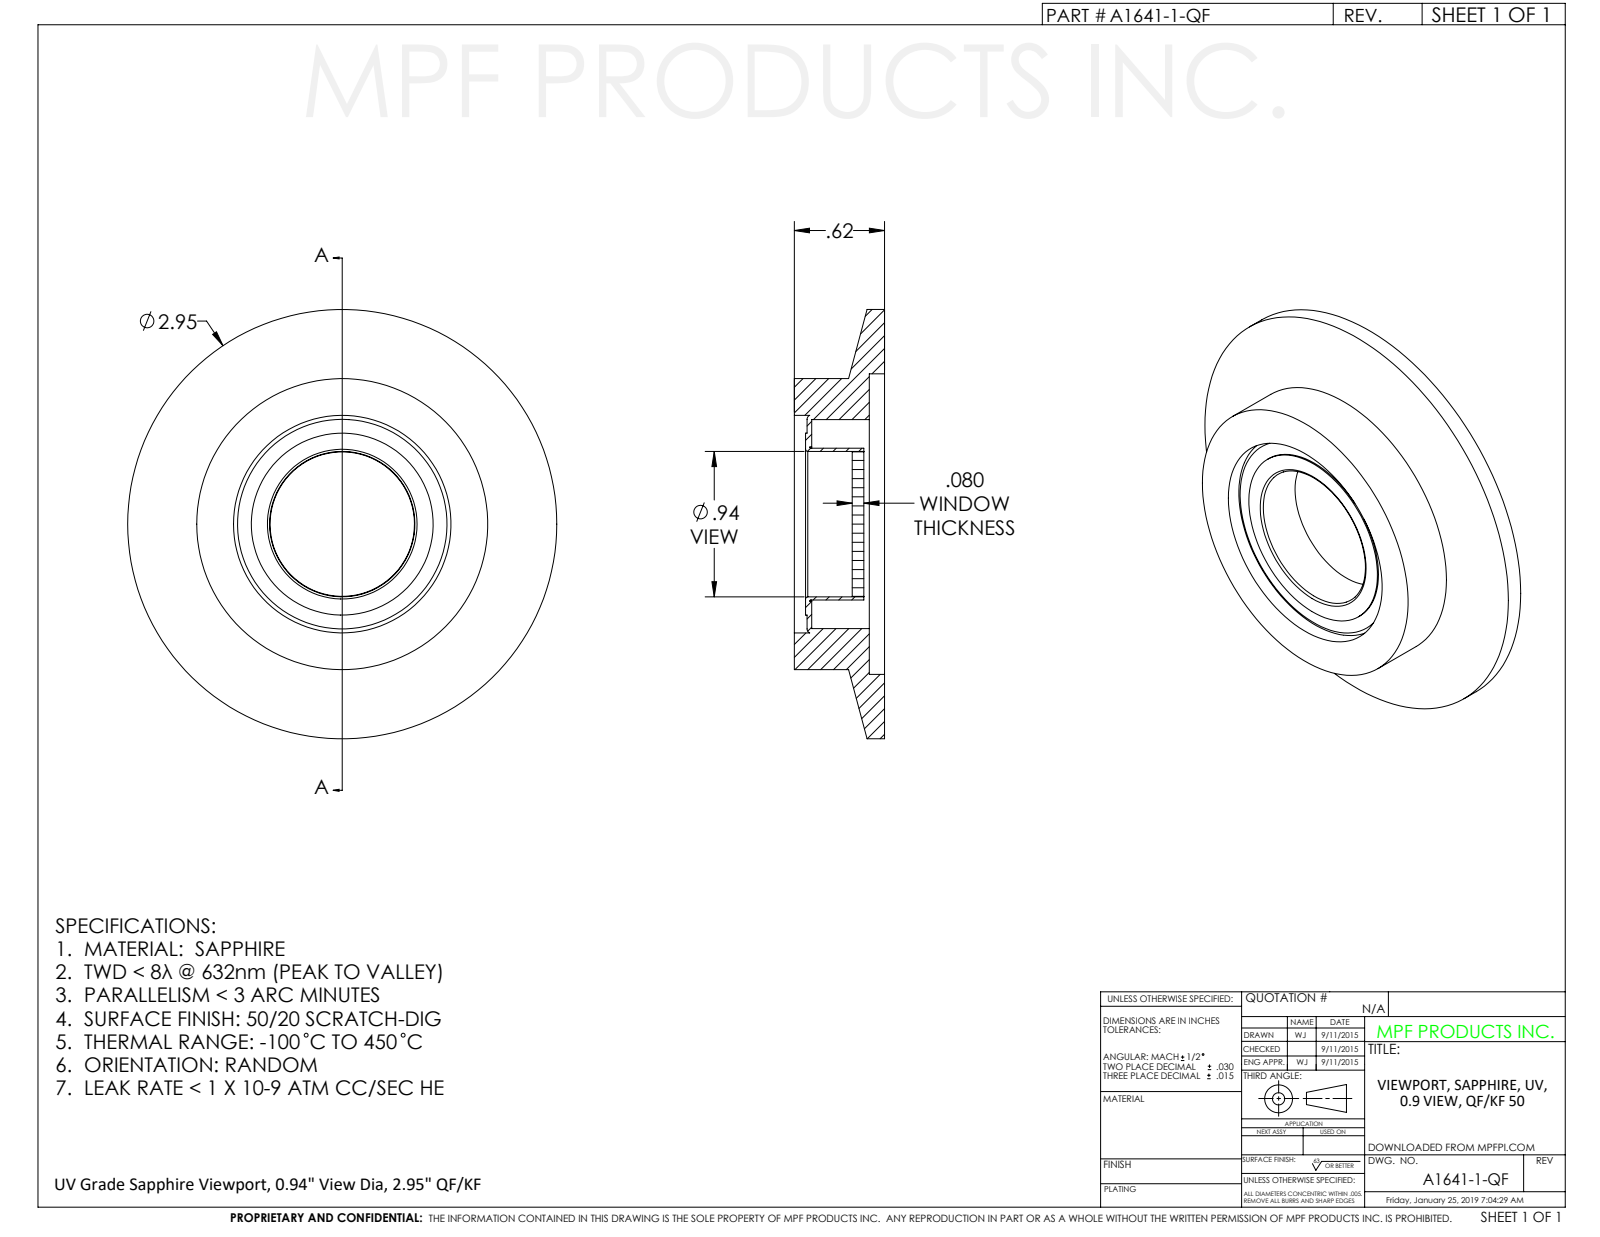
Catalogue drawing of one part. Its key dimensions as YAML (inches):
part_name: "A1641-1-QF"
step_written_by: "SolidWorks 2019 (CONFIG_CONTROL_DESIGN)"
units: inches
bodies: {solids: 1, faces: 41, planar: 11, cylindrical: 22, other: 8}
overall_size: [2.95, 2.95, 0.62]
volume: 1.522
surface_area: 22.98
round_holes:
  - {diameter: 0.999, count: 1}
  - {diameter: 1.062, count: 1}
  - {diameter: 1.44, count: 1}
  - {diameter: 1.495, count: 1}
  - {diameter: 1.745, count: 1}
  - {diameter: 2.065, count: 1}
round_bosses_or_shafts:
  - {diameter: 2.95, count: 1}
  - {diameter: 2, count: 1}
  - {diameter: 1.545, count: 1}
  - {diameter: 1.25, count: 1}
  - {diameter: 1.059, count: 1}
face_to_face_distances: [0.62, 0.105, 0.515, 0.132, 0.027, 0.488, 0.212, 0.107, 0.08, 0.408]
